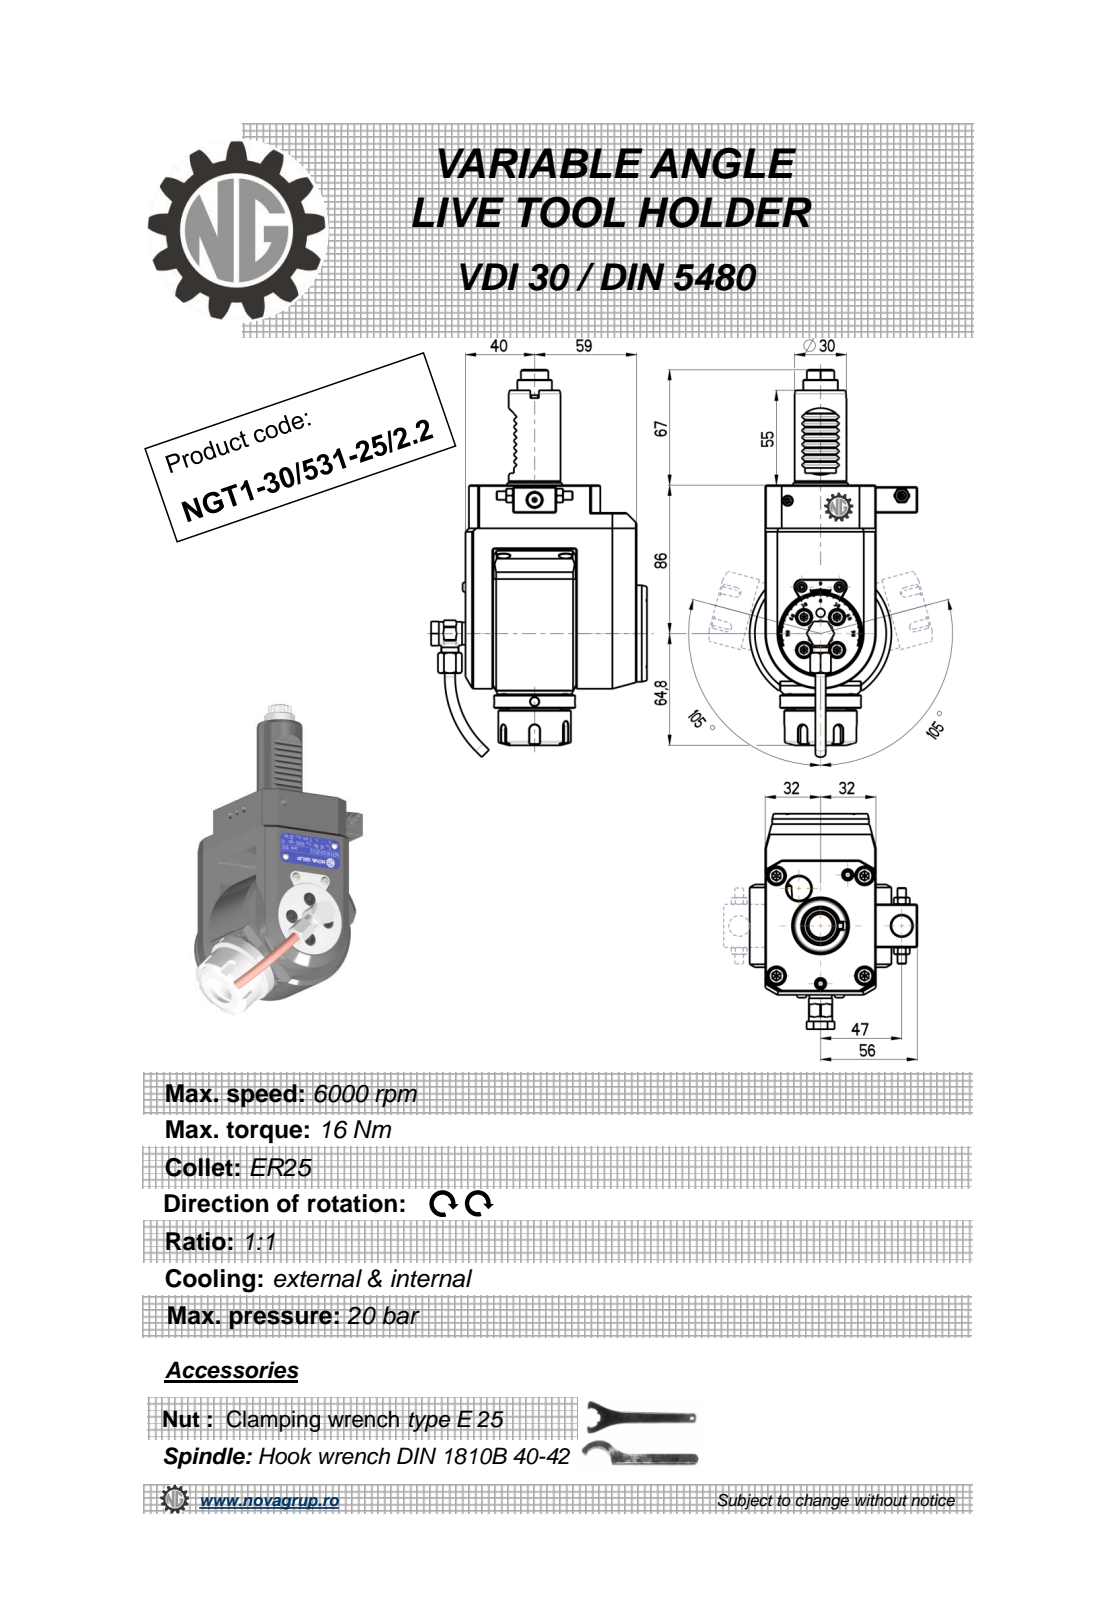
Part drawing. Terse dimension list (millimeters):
name: NGT1_30_531_25_2_2
written by: PRO/ENGINEER BY PARAMETRIC TECHNOLOGY CORPORATION, 2010280 (CONFIG_CONTROL_DESIGN)
unit: mm
bodies: 1 solid, 651 faces (239 planar, 209 cylindrical, 203 other)
size: 224.67 × 124.9 × 97
volume: 806 781 mm³; area: 76 392 mm²
holes: 3× ⌀4, 2× ⌀5, 1× ⌀3, 1× ⌀4.2, 1× ⌀6.2, 1× ⌀9, 1× ⌀9.5, 1× ⌀11, 1× ⌀12, 1× ⌀20.3
bosses: 2× ⌀10, 2× ⌀6, 2× ⌀5.7, 1× ⌀56, 1× ⌀47, 1× ⌀42, 1× ⌀35, 1× ⌀30
rounds: 36× R1.98, 12× R0.26, 8× R0.3, 6× R0.16, 5× R3, 4× R0.5, 2× R1, 1× R7.29
face distances: 64, 16, 37, 6, 99, 105, 21, 14, 62, 83
hole spacings: 0.4, 39.45, 47, 49, 49.4, 67.9, 68.19, 92.78
